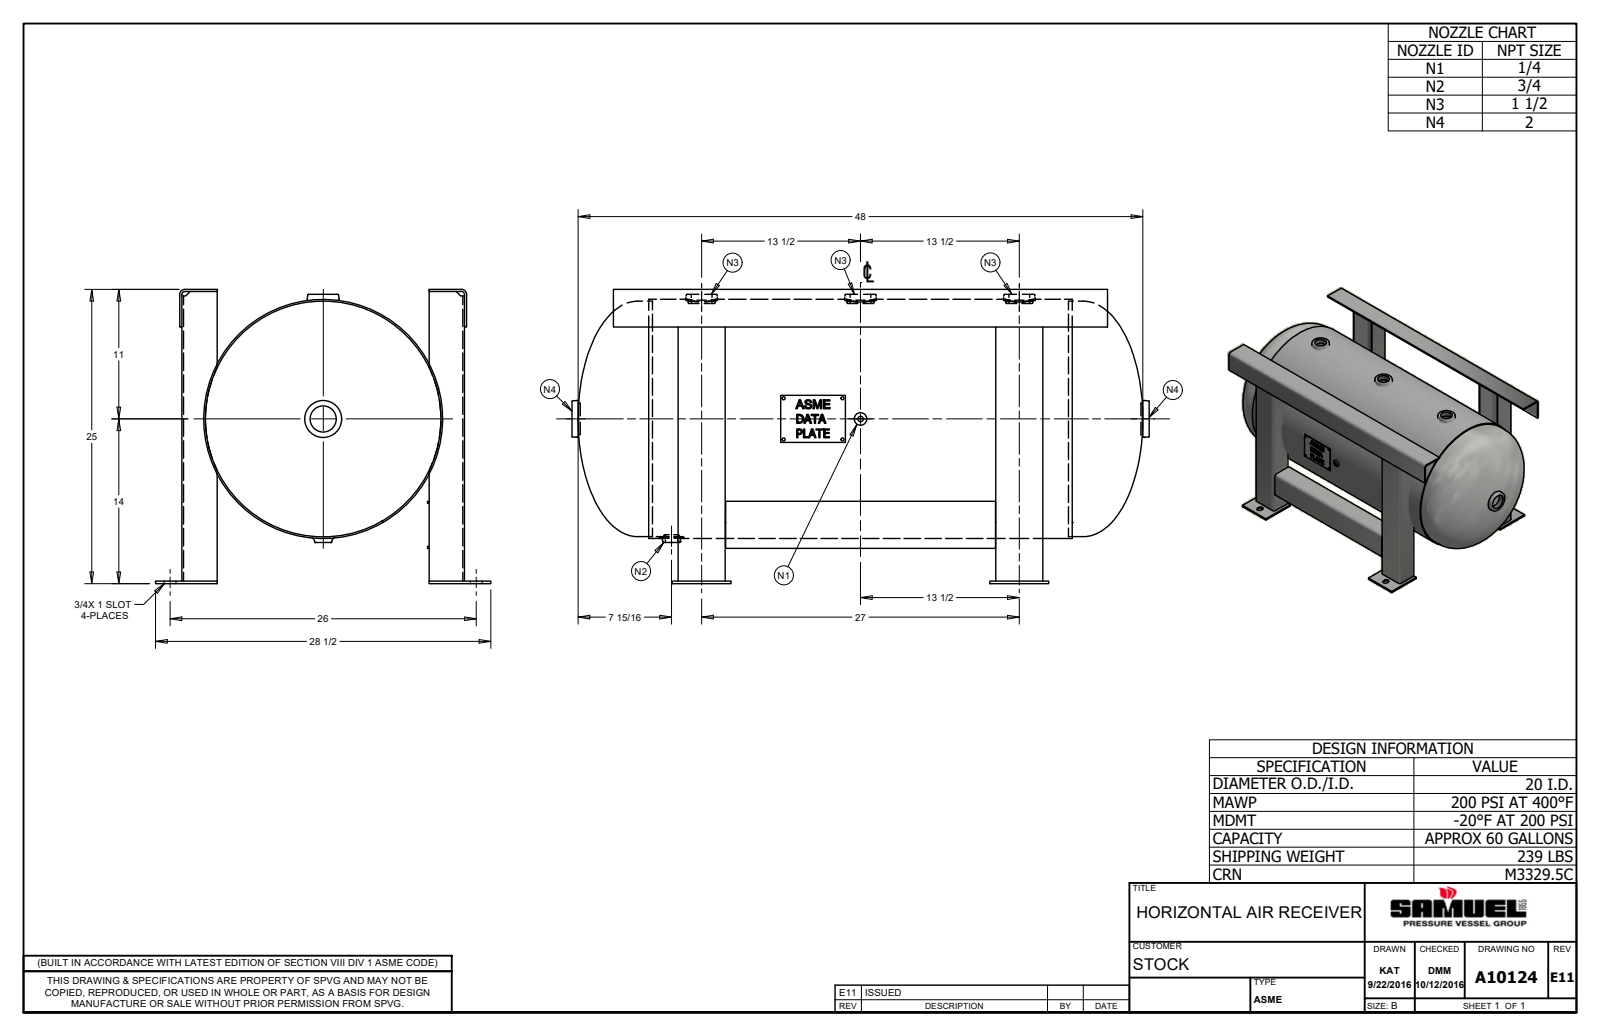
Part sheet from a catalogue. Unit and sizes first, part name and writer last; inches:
Units: inches
Overall size (bounding box): 49.063 × 28.511 × 24.999
Round holes (diameter × count): ⌀0.25 ×4, ⌀1.766 ×3, ⌀2.375 ×3, ⌀0.451 ×1, ⌀1.063 ×1, ⌀1.437 ×1, ⌀2.231 ×1, ⌀2.687 ×1, ⌀19.752 ×1
Round bosses / shafts (diameter × count): ⌀2.687 ×3, ⌀2.266 ×3, ⌀20.312 ×1, ⌀20 ×1, ⌀3.125 ×1, ⌀2.063 ×1, ⌀1.453 ×1
Partial cylindrical surfaces — rounded edges, fillets, slot ends (radius × count): R0.322 ×8, R0.375 ×8, R0.25 ×6, R0.429 ×6, R0.187 ×4, R0.188 ×4, R10.062 ×2, R7.5 ×1
Main face-to-face distances: 0.179, 27, 0.135, 3.865, 23.877, 0.134, 4, 0.18, 0.314, 24.011
Hole centre spacings: 2.325, 3.5, 5, 6.103, 6.761, 13.5, 2.563, 16.063
Volume: 799.6 in³ · Surface area: 10 689 in²
Bodies: 23 solids, 458 faces (298 planar, 80 cylindrical, 80 other)
Part name (STEP PRODUCT): A10124; A10124-1; A10124-2; 910-800 (+8 more)
STEP written by: Autodesk Inventor 2019 (CONFIG_CONTROL_DESIGN)
